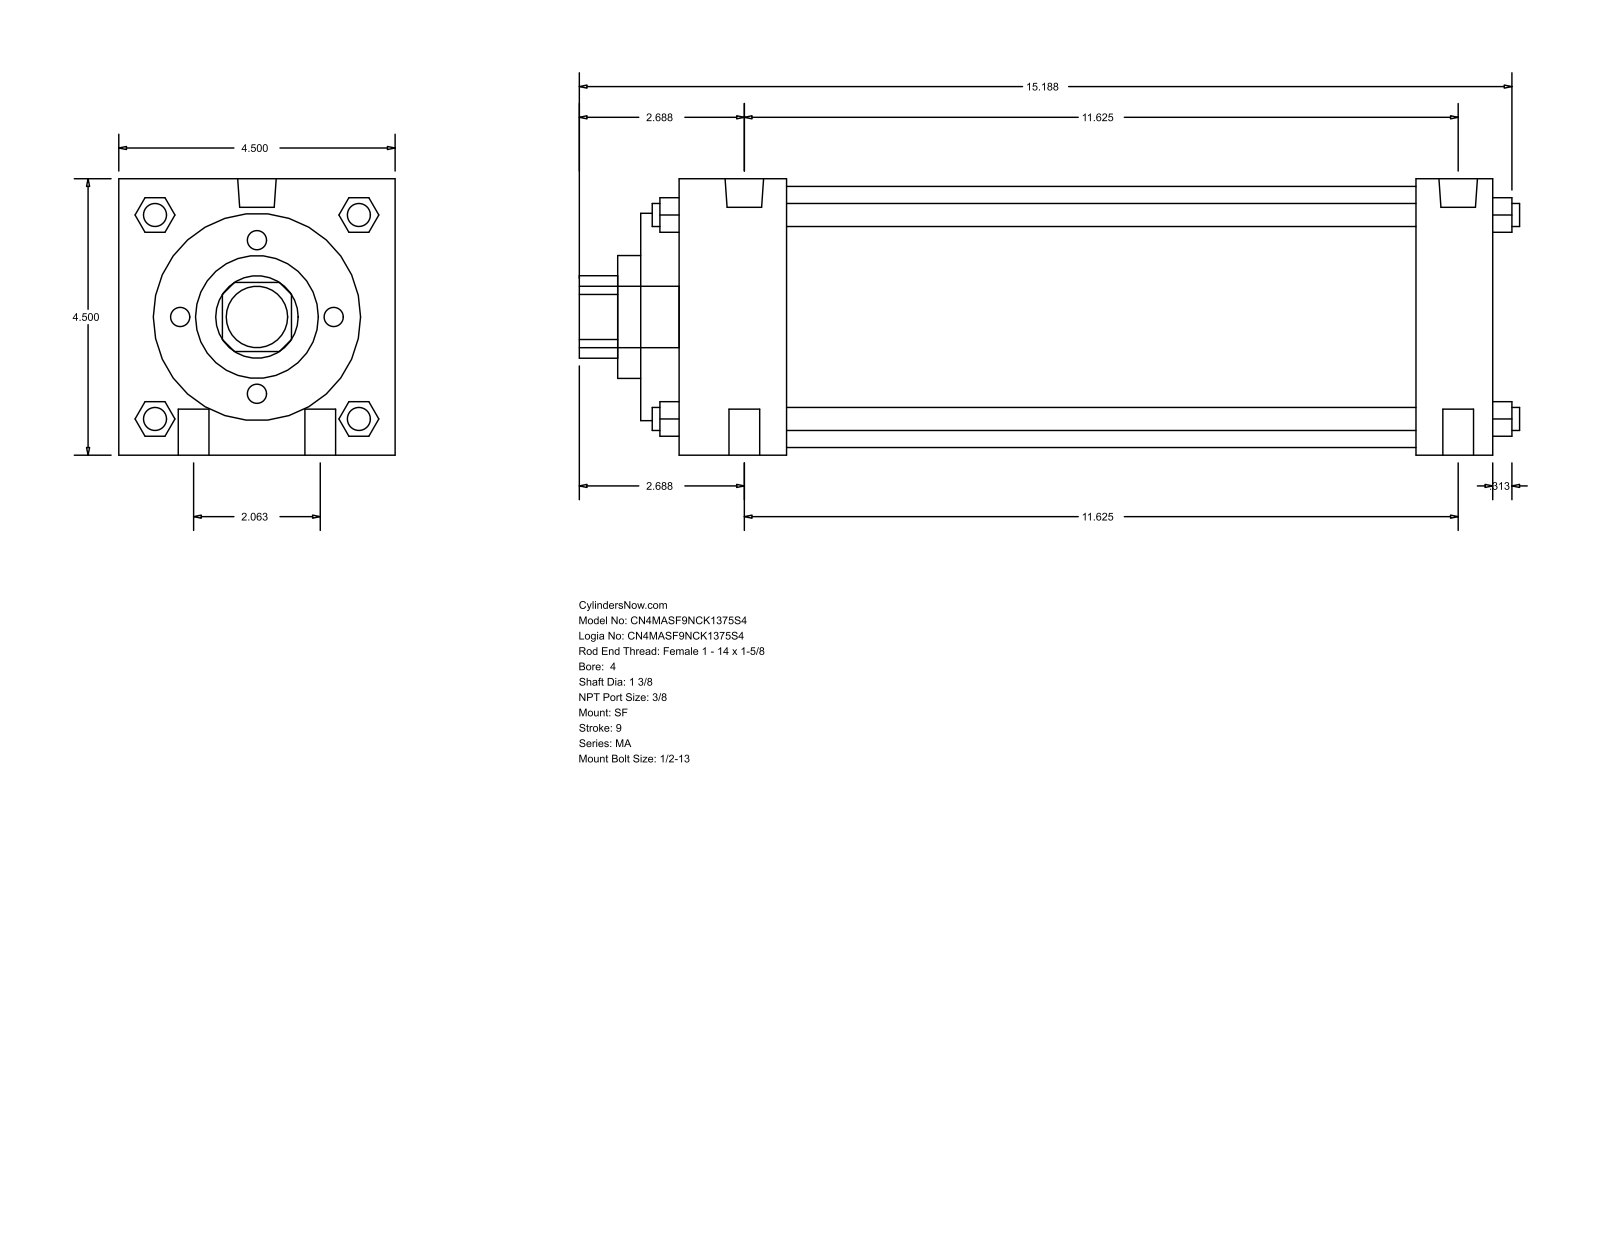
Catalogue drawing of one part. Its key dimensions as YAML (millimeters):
part_name: "MA_SF__0400_1.375"
step_written_by: "GSSL Pune (CONFIG_CONTROL_DESIGN)"
units: millimeters
bodies: {solids: 0, faces: 126, planar: 95, cylindrical: 31, other: 0}
overall_size: [388.94, 114.3, 114.3]
round_holes:
  - {diameter: 34.92, count: 1}
  - {diameter: 50.8, count: 1}
  - {diameter: 85.72, count: 1}
  - {diameter: 107.95, count: 1}
round_bosses_or_shafts:
  - {diameter: 12.7, count: 4}
  - {diameter: 9.53, count: 4}
  - {diameter: 15.93, count: 2}
  - {diameter: 11.11, count: 2}
  - {diameter: 25.4, count: 1}
partial_cylinders:
  - {radius: 17.06, count: 1}
face_to_face_distances: [114.3, 336.55, 352.42, 15.87, 320.67, 304.8, 31.75, 60.32, 44.45, 260.35]
